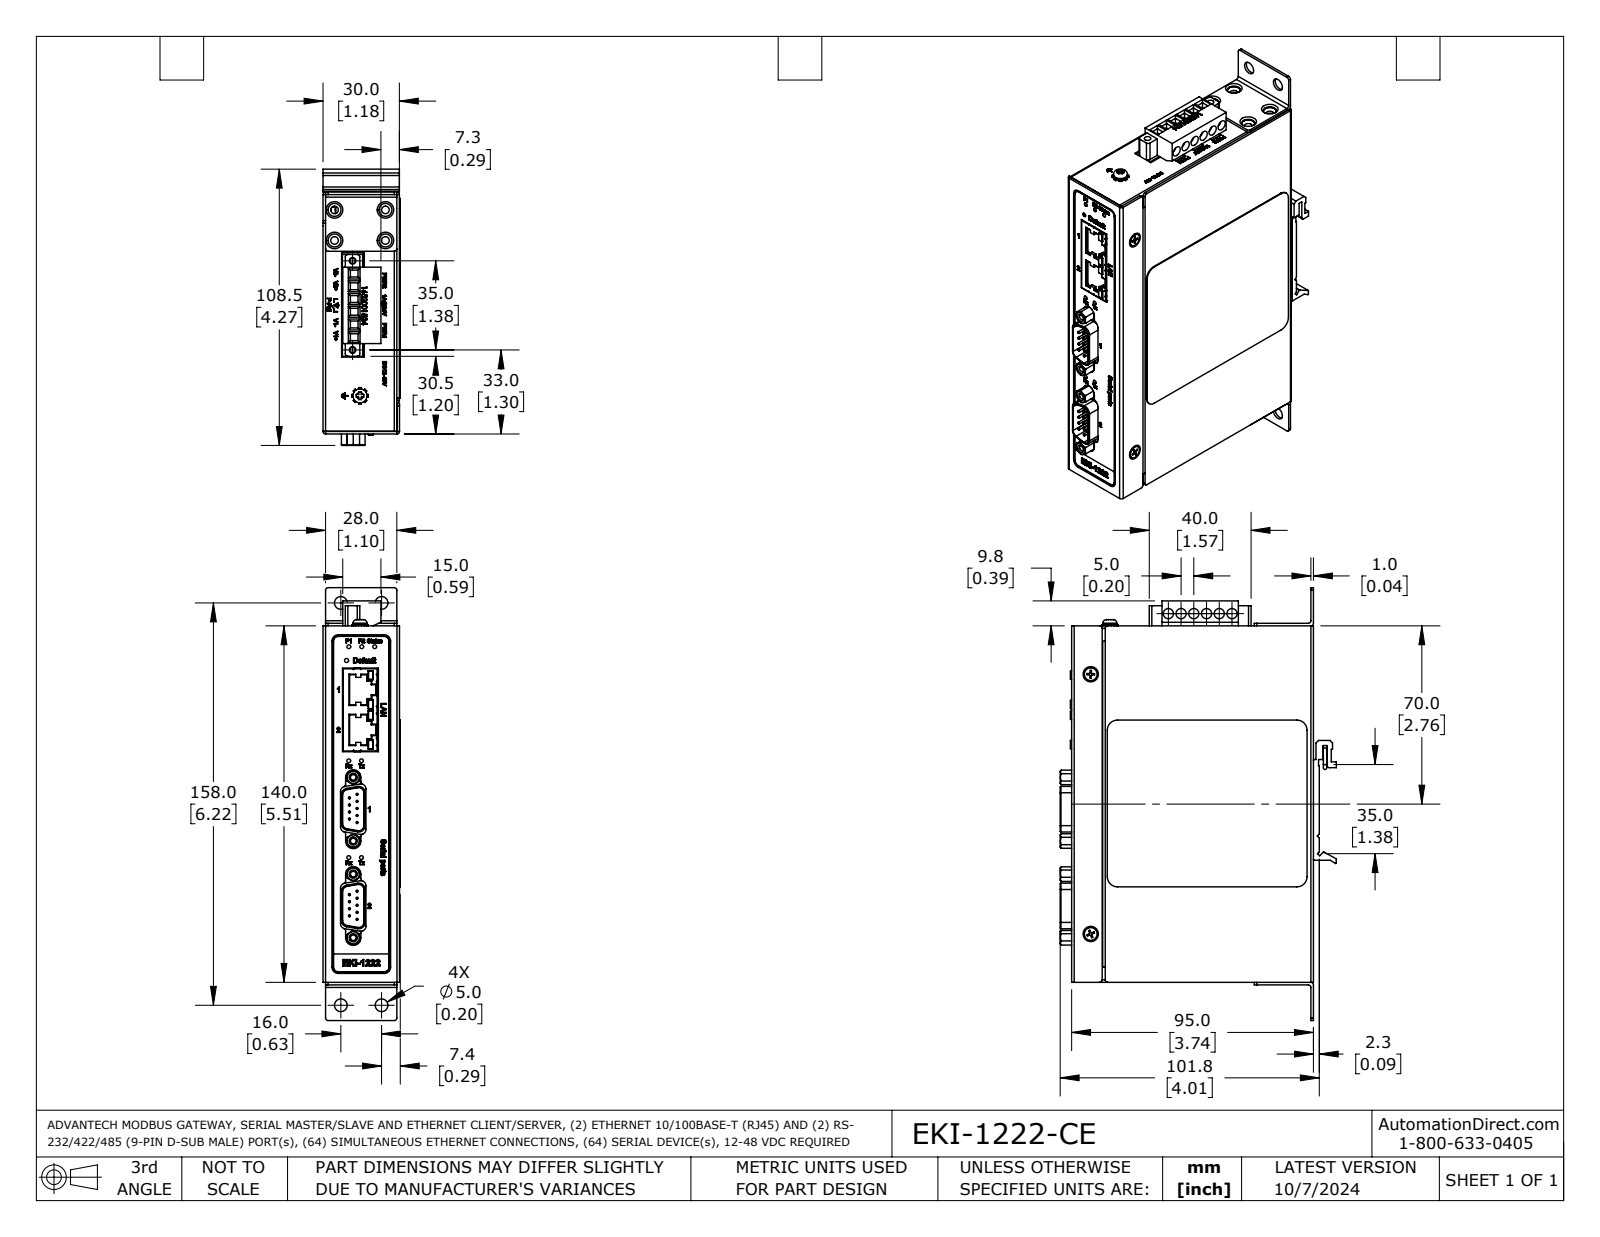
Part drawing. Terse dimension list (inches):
name: EKI-1222-CE
written by: SolidWorks 2021 (AUTOMOTIVE_DESIGN)
unit: in
bodies: 14 solids, 2361 faces (1383 planar, 430 cylindrical, 548 other)
size: 6.693 × 4.272 × 1.195
volume: 22.4 in³; area: 171.2 in²
holes: 15× ⌀0.138, 13× ⌀0.059, 9× ⌀0.118, 6× ⌀0.157, 4× ⌀0.087, 4× ⌀0.197, 4× ⌀0.201, 2× ⌀0.081, 2× ⌀0.102, 1× ⌀0.063, 1× ⌀0.098
bosses: 18× ⌀0.031, 9× ⌀0.197, 6× ⌀0.051, 3× ⌀0.112, 1× ⌀0.217, 1× ⌀0.118, 1× ⌀0.112
rounds: 49× R0.039, 28× R0.014, 16× R0.079, 14× R0.098, 8× R0.012, 6× R0.11, 5× R0.02, 4× R0.073
face distances: 0.039, 1.142, 1.181, 0.014, 0.041, 1.195, 0.053, 1.1, 1.102, 3.72
hole spacings: 0.197, 0.394, 0.591, 0.787, 0.984, 1.496, 0.265, 0.285
